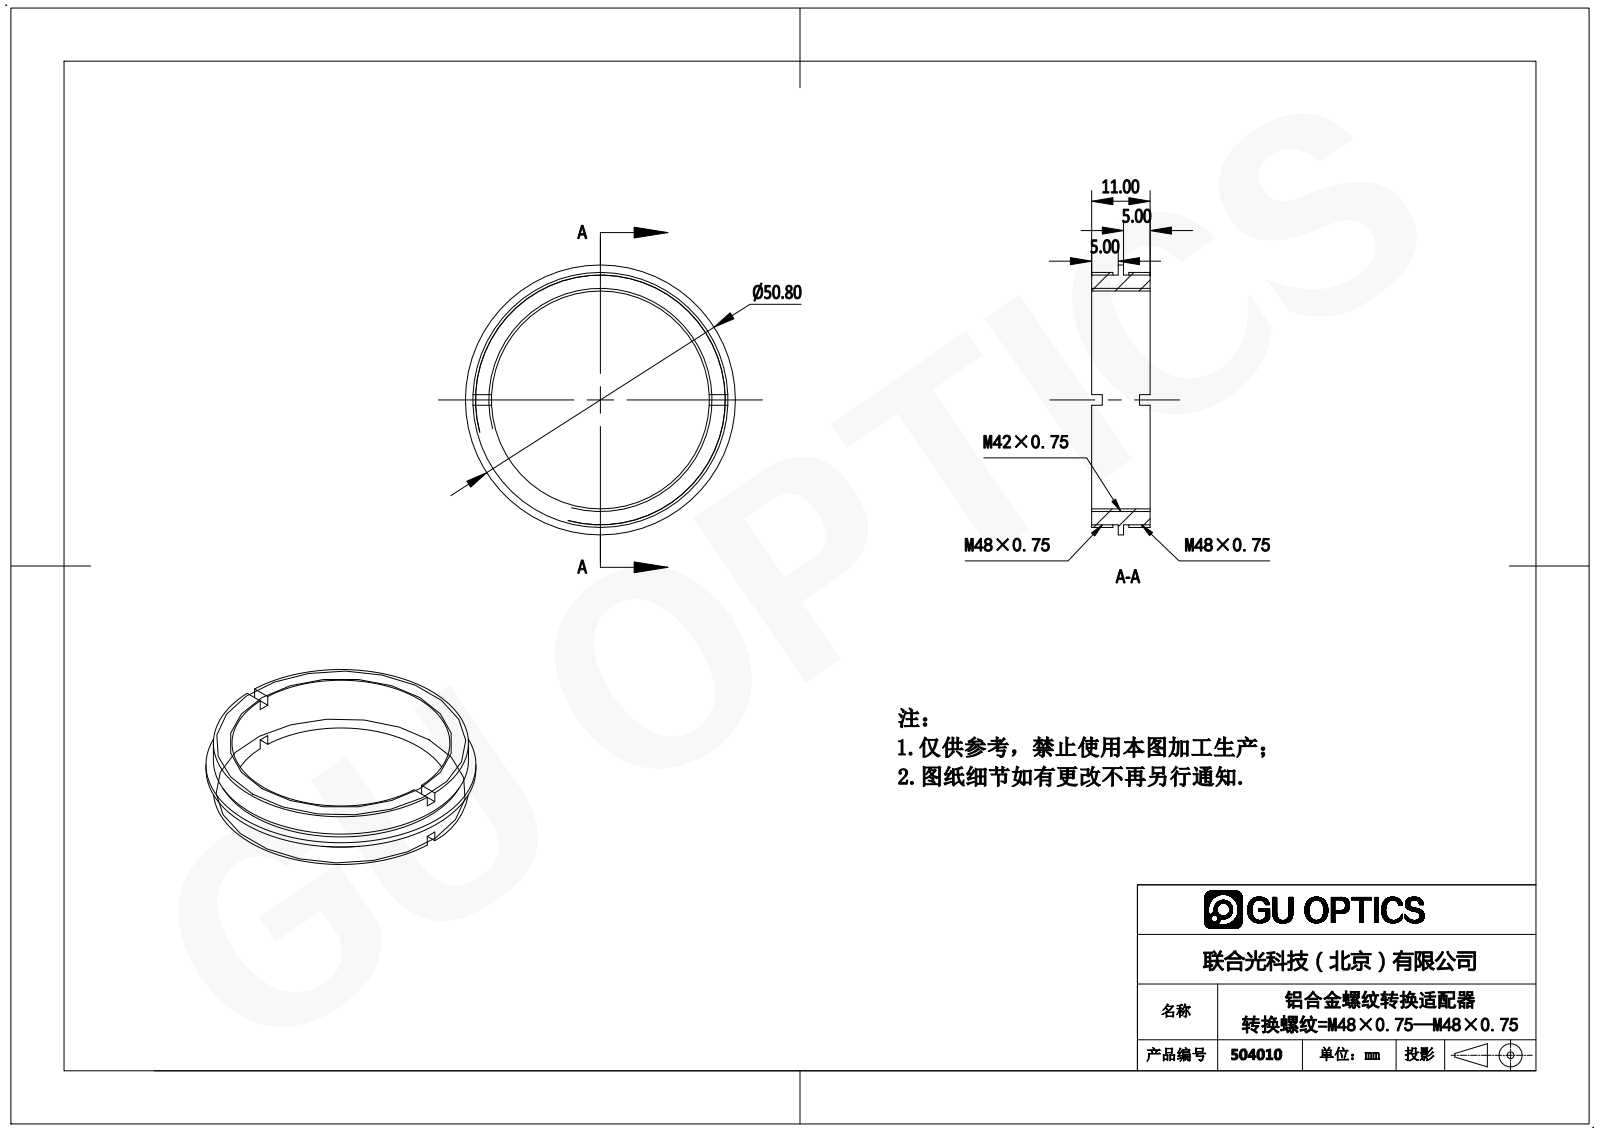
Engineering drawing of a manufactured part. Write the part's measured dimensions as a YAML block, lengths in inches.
part_name: "504010"
step_written_by: "SolidWorks 2016 (AUTOMOTIVE_DESIGN)"
units: inches
bodies: {solids: 1, faces: 32, planar: 20, cylindrical: 12, other: 0}
overall_size: [2, 2, 0.433]
volume: 0.329
surface_area: 7.462
round_holes:
  - {diameter: 1.614, count: 1}
round_bosses_or_shafts:
  - {diameter: 2, count: 1}
  - {diameter: 1.89, count: 1}
  - {diameter: 1.85, count: 1}
face_to_face_distances: [0.197, 0.236, 0.433, 0.039, 0.079, 0.157, 0.276, 0.118, 0.354]
